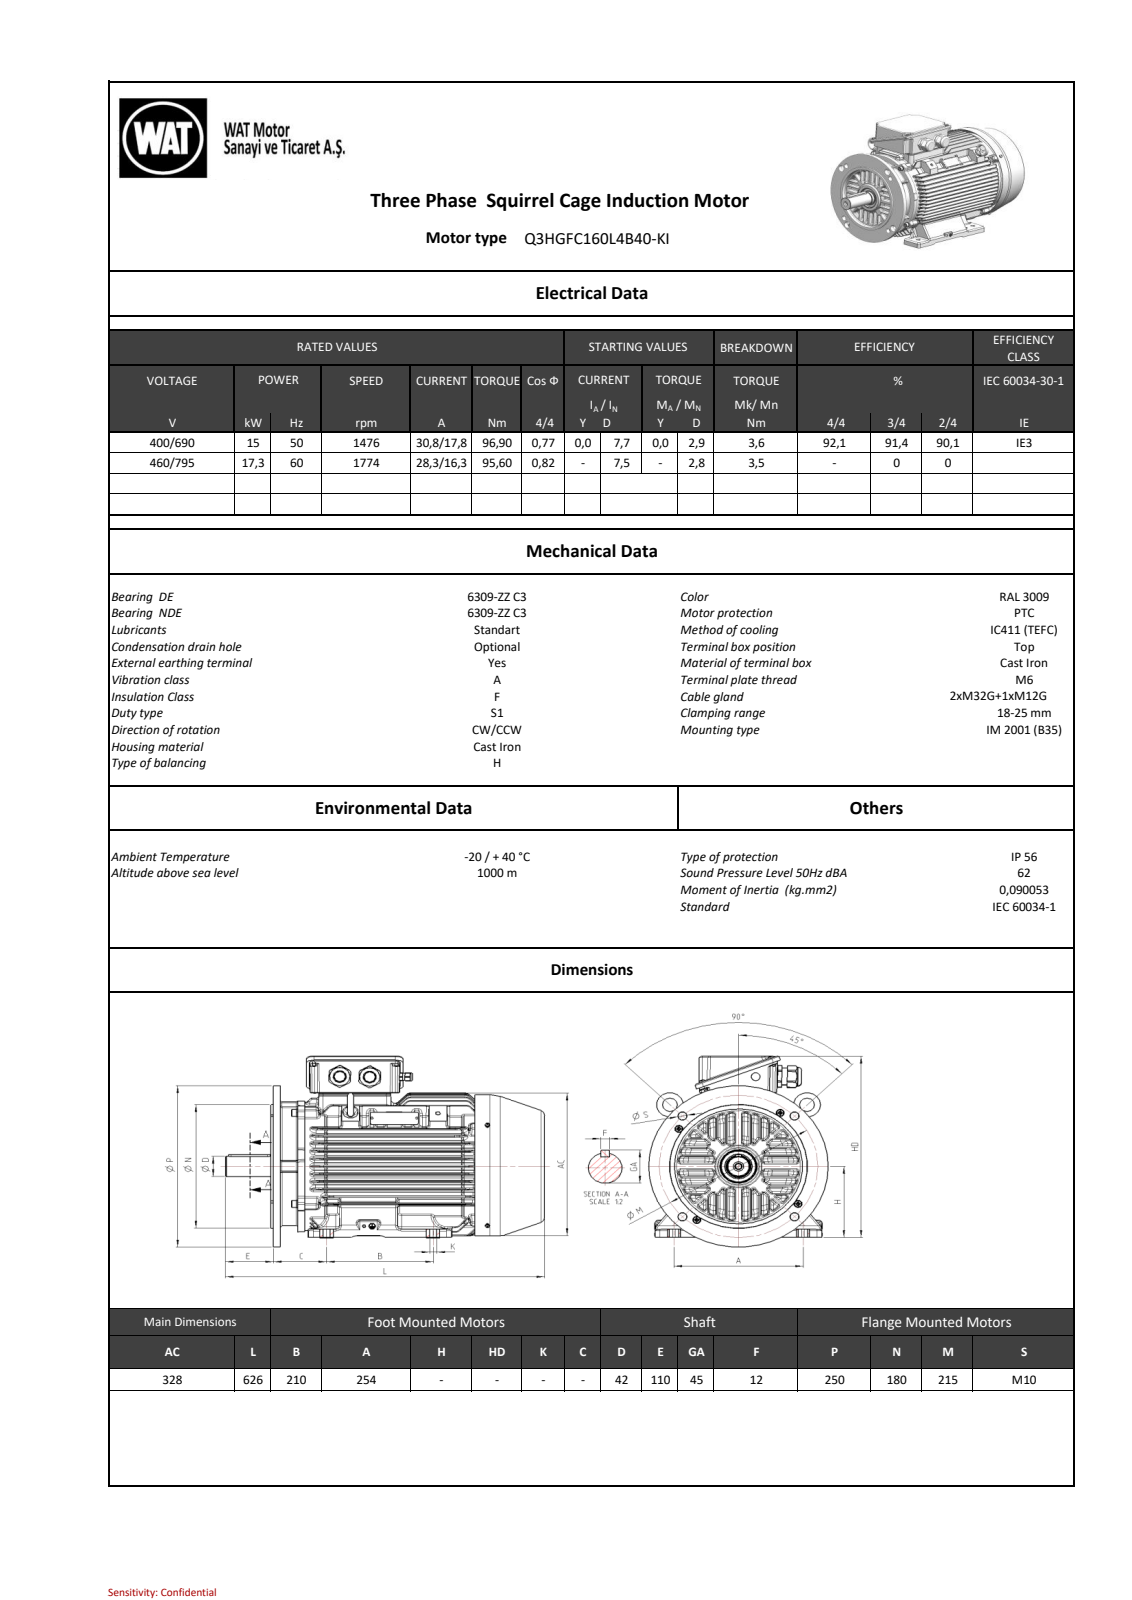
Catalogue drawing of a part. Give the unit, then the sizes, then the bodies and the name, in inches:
Units: inches
Overall size (bounding box): 24.626 × 15.397 × 12.889
Round holes (diameter × count): ⌀0.217 ×8, ⌀0.354 ×8, ⌀0.165 ×6, ⌀0.429 ×6, ⌀0.209 ×4, ⌀0.335 ×4, ⌀0.098 ×2, ⌀0.205 ×2, ⌀0.748 ×2, ⌀0.827 ×2, ⌀0.394 ×1, ⌀0.551 ×1
Round bosses / shafts (diameter × count): ⌀0.63 ×8, ⌀0.787 ×4, ⌀1.358 ×2, ⌀1.23 ×2, ⌀1.181 ×2, ⌀0.394 ×2, ⌀12.48 ×1, ⌀11.102 ×1
Partial cylindrical surfaces — rounded edges, fillets, slot ends (radius × count): R0.197 ×187, R0.059 ×112, R0.118 ×109, R0.138 ×71, R0.079 ×67, R0.157 ×66, R0.071 ×54, R0.039 ×36
Main face-to-face distances: 0.597, 5.411, 1.198, 0.6, 4.811, 1.8, 4.208, 1.203, 0.603, 2.406
Hole centre spacings: 5.354, 1.672, 5.669, 6.459, 7.641, 8.018, 9.865, 2.745
Bodies: 0 solids, 5343 faces (1024 planar, 1442 cylindrical, 2877 other)
Part name (STEP PRODUCT): 260052A4A387t53i
STEP written by: SIEMENS PLM Software NX 11.0 (AUTOMOTIVE_DESIGN)
